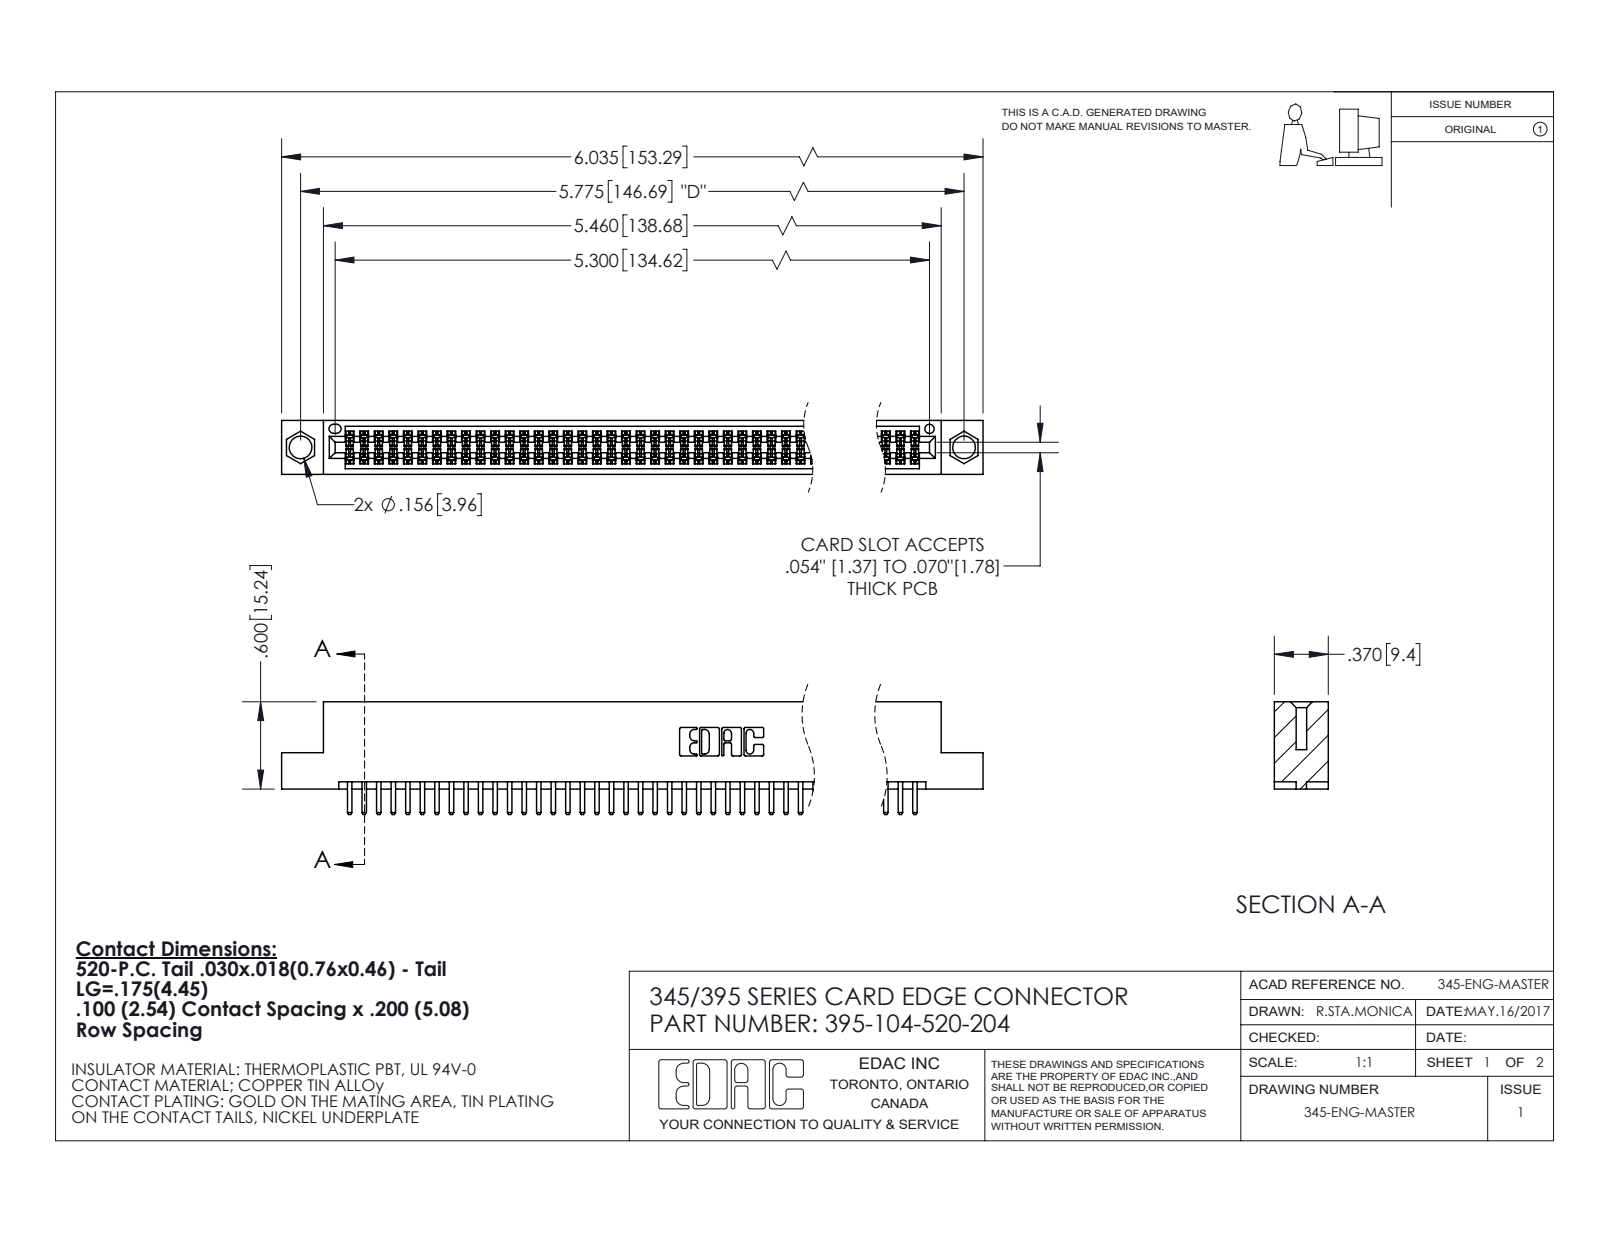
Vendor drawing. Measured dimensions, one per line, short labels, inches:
name: 345-292-001_345-293-120; 345 Part_Flush Mounting Lugs - 0.156 Dia-TI; 395-104-520-204
written by: SolidWorks 2020 (CONFIG_CONTROL_DESIGN)
unit: in
bodies: 105 solids, 5756 faces (3734 planar, 2022 cylindrical, 0 other)
size: 6.035 × 0.775 × 0.37
volume: 0.905 in³; area: 33.9 in²
holes: 2× ⌀0.156, 1× ⌀0.064
rounds: 156× R0.006, 108× R0.01, 22× R0.01, 6× R0.007, 6× R0.031, 3× R0.026, 2× R0.014, 2× R0.019
face distances: 0.298, 0.072, 0.2, 0.37, 0.098, 0.272, 0.025, 0.225, 0.022, 0.072
hole spacings: 0.27, 5.539, 5.775
